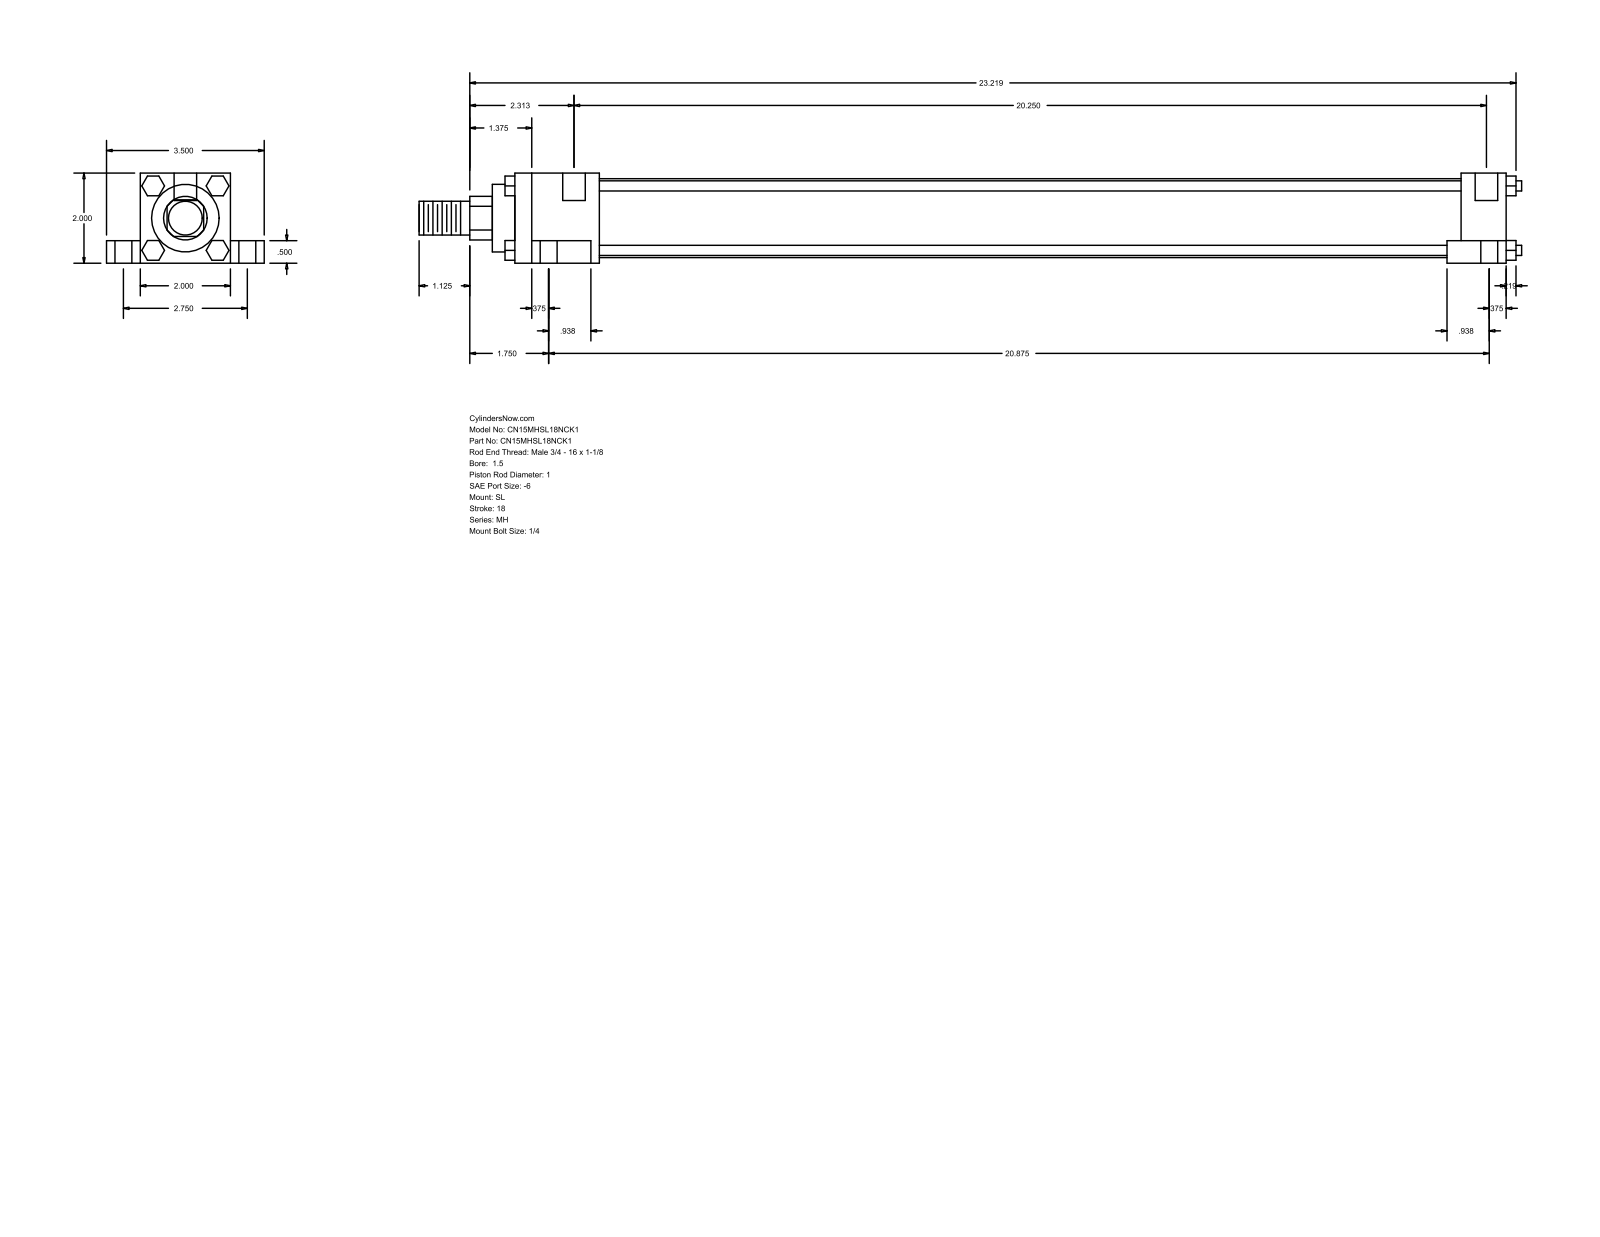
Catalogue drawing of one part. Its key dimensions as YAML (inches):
part_name: "MH_SL__0150_1"
step_written_by: "GSSL Pune (CONFIG_CONTROL_DESIGN)"
units: inches
bodies: {solids: 0, faces: 148, planar: 112, cylindrical: 36, other: 0}
overall_size: [24.469, 3.5, 2]
round_holes:
  - {diameter: 0.219, count: 4}
  - {diameter: 0.375, count: 4}
  - {diameter: 0.625, count: 4}
  - {diameter: 0.5, count: 2}
round_bosses_or_shafts:
  - {diameter: 0.225, count: 4}
  - {diameter: 1.75, count: 1}
  - {diameter: 1.5, count: 1}
  - {diameter: 1, count: 1}
  - {diameter: 0.75, count: 1}
partial_cylinders:
  - {radius: 0.484, count: 1}
face_to_face_distances: [2, 0.5, 1.5, 0.75, 2.75, 22, 1, 0.375, 1.313, 20.313]
hole_center_spacings: [1.376, 1.443, 1.485, 2.75, 20.359, 20.375, 20.483, 20.858]
